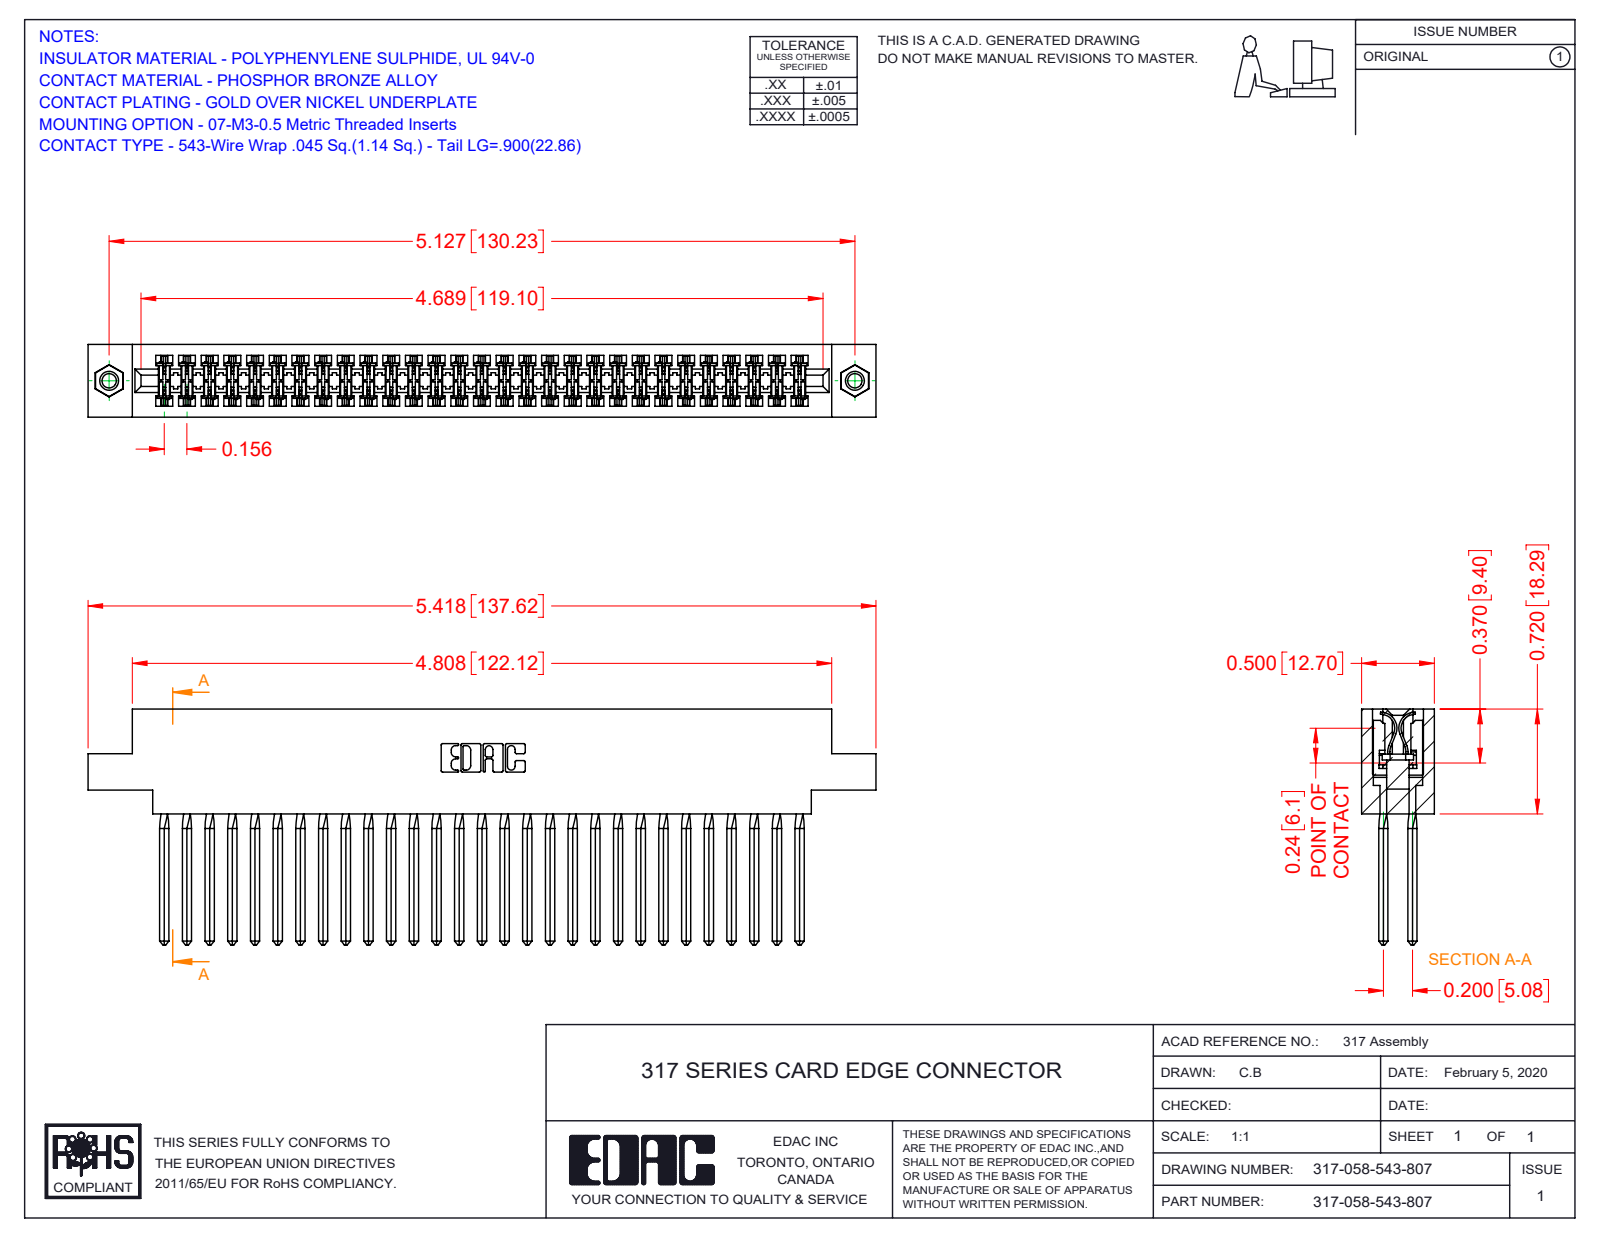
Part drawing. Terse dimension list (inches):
name: 317 Part_.156 Dia - TI; 317-290-001_543; 345-250-001_345-250-005-103; 317-058-543-807
written by: SolidWorks 2016 (CONFIG_CONTROL_DESIGN)
unit: in
bodies: 61 solids, 5324 faces (4324 planar, 752 cylindrical, 248 other)
size: 5.418 × 1.62 × 0.5
volume: 1.399 in³; area: 53.19 in²
holes: 2× ⌀0.098, 2× ⌀0.125, 2× ⌀0.156
bosses: 2× ⌀0.155
rounds: 116× R0.015, 22× R0.01, 6× R0.007, 6× R0.031, 3× R0.026, 2× R0.095, 2× R0.1, 2× R0.11
face distances: 0.5, 0.075, 0.425, 0.35, 0.11, 0.195, 0.094, 0.2, 0.72, 0.115
hole spacings: 5.127
